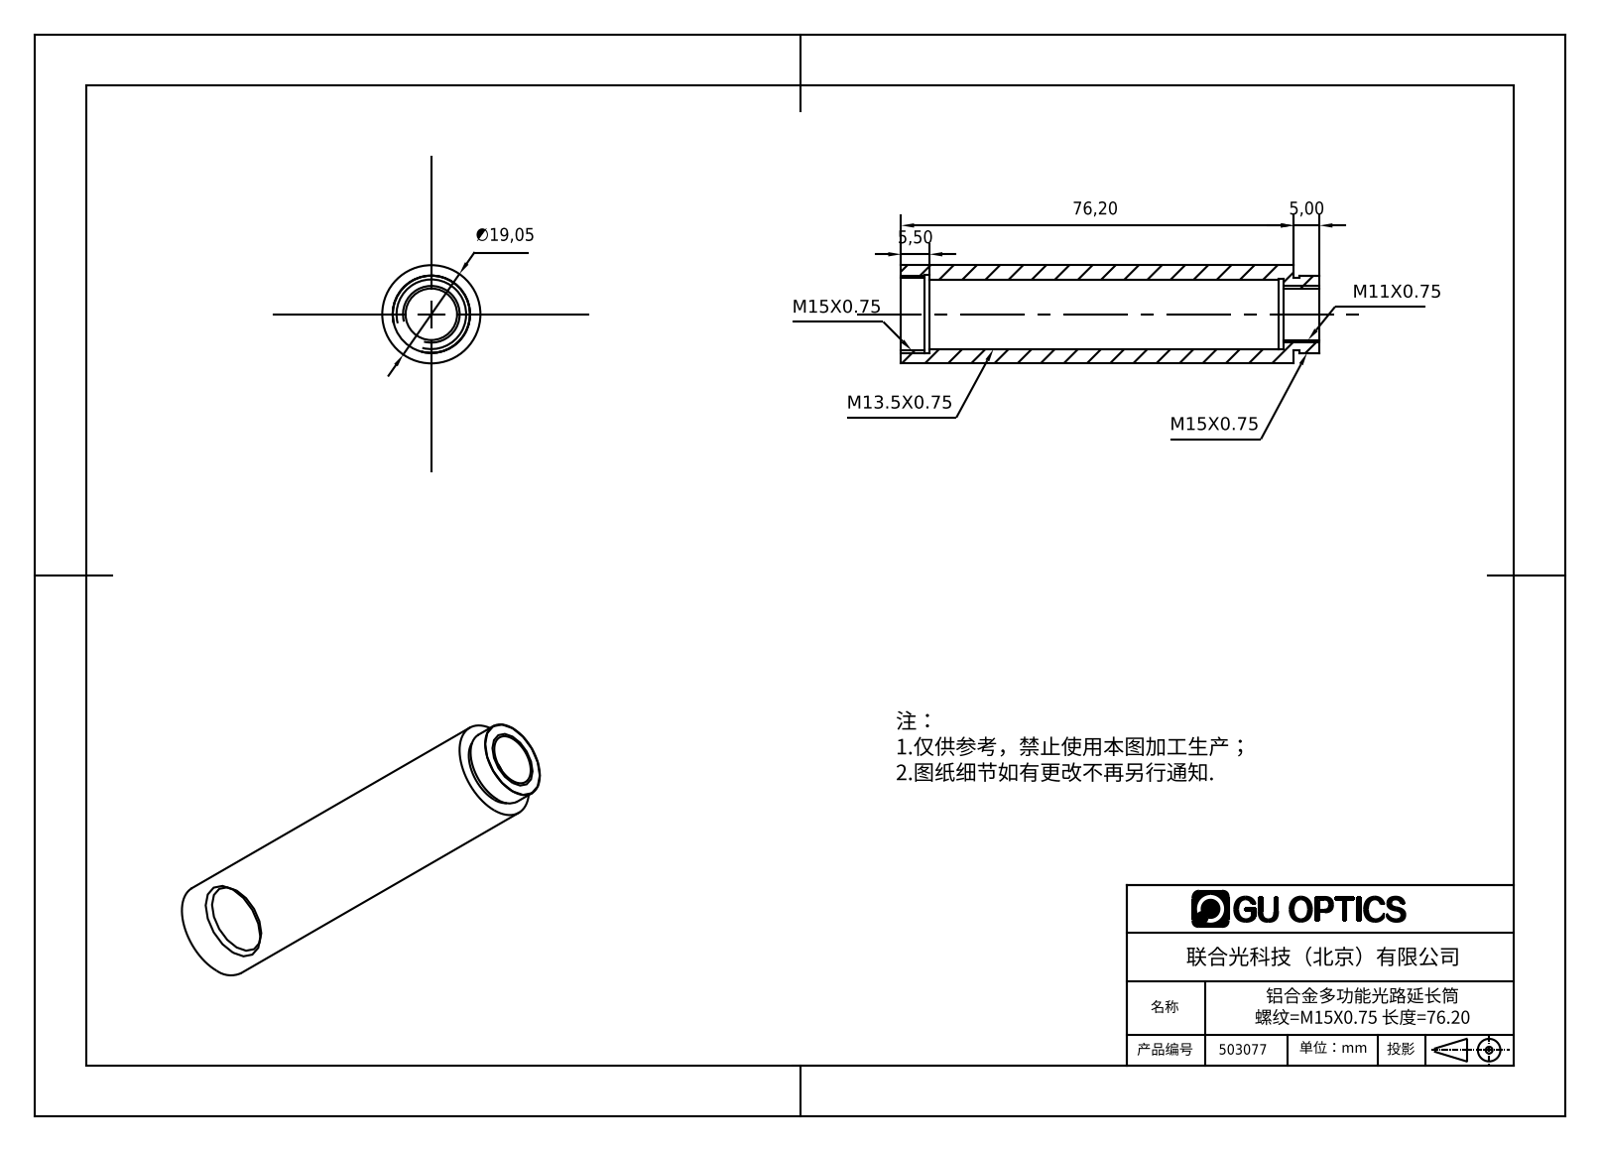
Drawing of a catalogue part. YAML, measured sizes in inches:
part_name: "503077"
step_written_by: "SolidWorks 2016 (AUTOMOTIVE_DESIGN)"
units: inches
bodies: {solids: 1, faces: 24, planar: 8, cylindrical: 16, other: 0}
overall_size: [3.197, 0.75, 0.75]
volume: 0.691
surface_area: 13.48
round_holes:
  - {diameter: 0.394, count: 1}
  - {diameter: 0.531, count: 1}
  - {diameter: 0.539, count: 1}
  - {diameter: 0.551, count: 1}
  - {diameter: 0.598, count: 1}
round_bosses_or_shafts:
  - {diameter: 0.75, count: 1}
  - {diameter: 0.591, count: 1}
face_to_face_distances: [3, 3.197, 0.197, 2.921, 0.079, 0.276, 0.039, 2.823, 2.705, 0.217]
